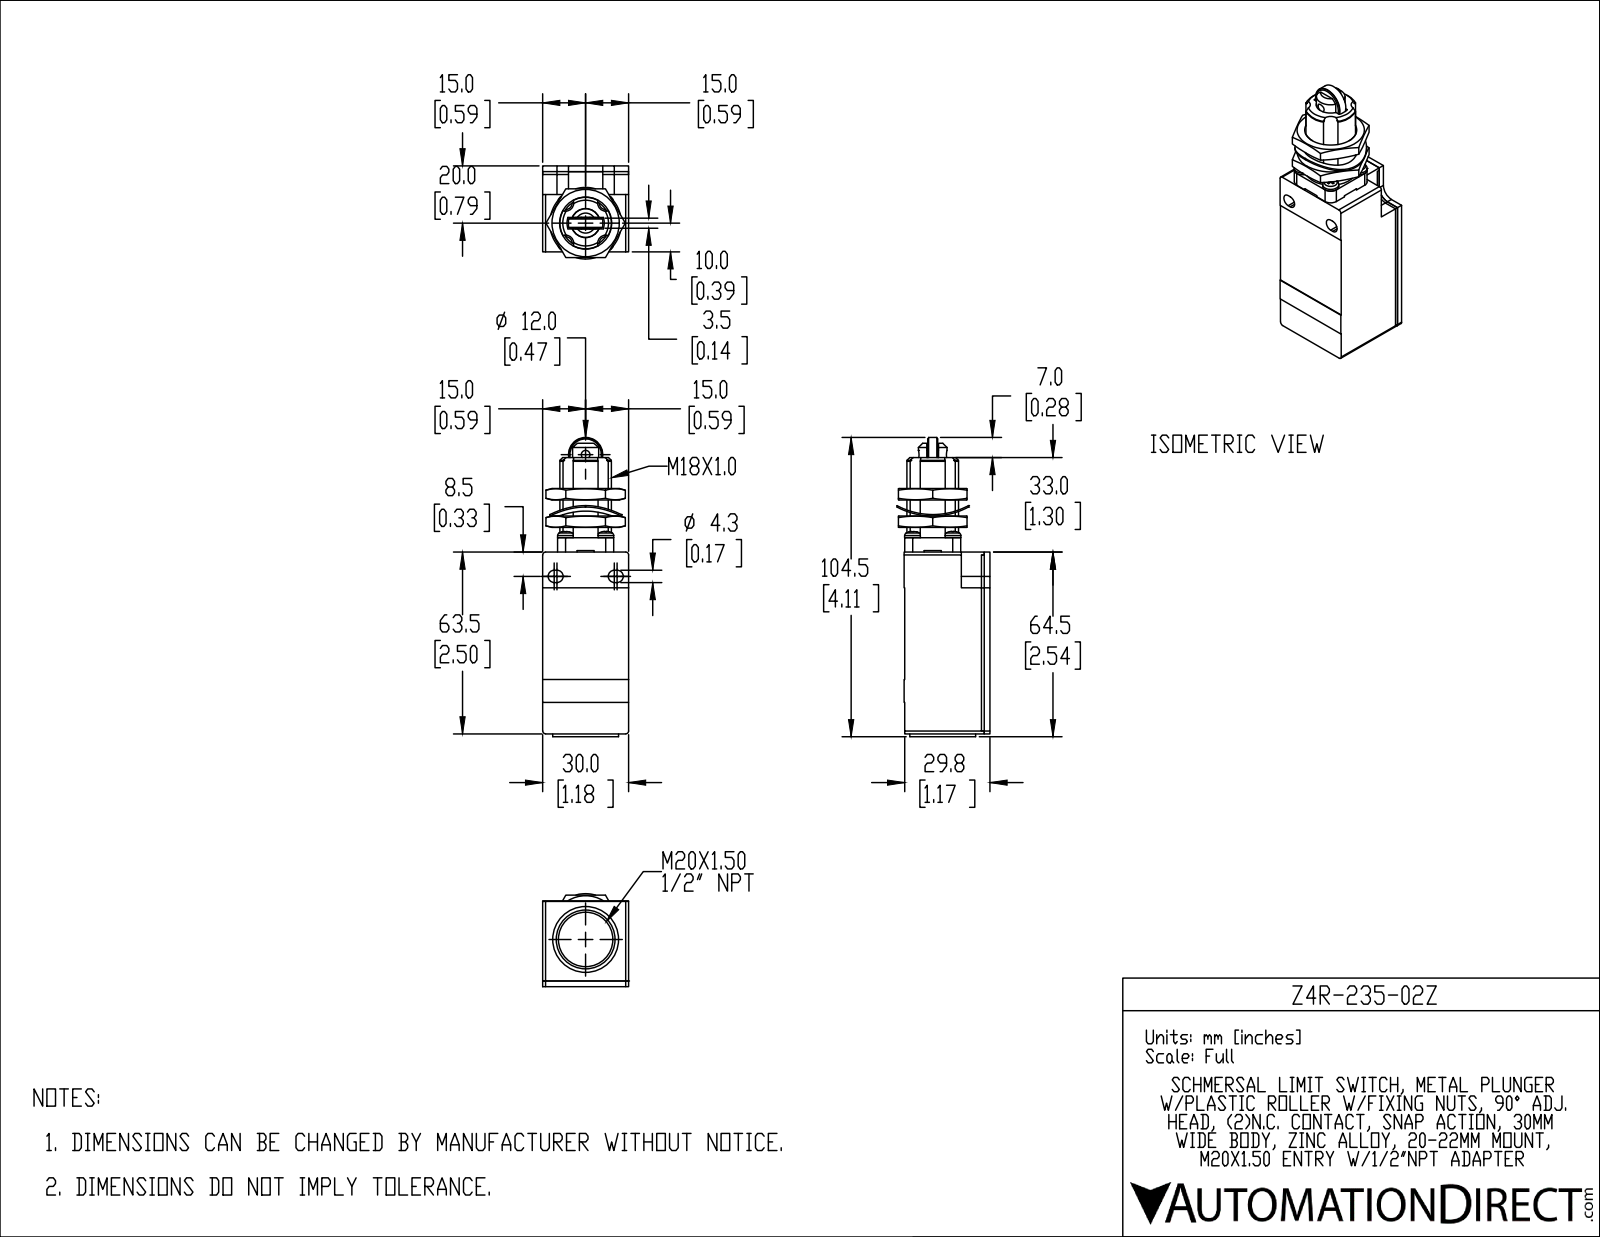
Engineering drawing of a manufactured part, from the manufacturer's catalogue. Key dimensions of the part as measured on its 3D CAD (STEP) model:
Part name (STEP PRODUCT): Z4R-235-02Z
STEP written by: SolidWorks 2019 (AUTOMOTIVE_DESIGN)
Units: inches
Bodies: 2 solids, 388 faces (264 planar, 95 cylindrical, 29 other)
Overall size (bounding box): 4.114 × 1.279 × 1.181
Volume: 3.806 in³ · Surface area: 26.23 in²
Round holes (diameter × count): ⌀0.276 ×3, ⌀0.118 ×1, ⌀0.512 ×1, ⌀0.545 ×1, ⌀0.732 ×1, ⌀0.748 ×1
Round bosses / shafts (diameter × count): ⌀0.213 ×4, ⌀0.256 ×3, ⌀0.984 ×1, ⌀0.906 ×1, ⌀0.472 ×1, ⌀0.415 ×1, ⌀0.394 ×1, ⌀0.276 ×1
Partial cylindrical surfaces — rounded edges, fillets, slot ends (radius × count): R0.02 ×12, R0.039 ×4, R0.085 ×4, R0.11 ×4, R0.11 ×4, R0.157 ×2, R0.159 ×2, R1.043 ×2
Main face-to-face distances: 1.181, 1.173, 0.157, 2.5, 0.079, 0.378, 0.945, 0.207, 2.293, 0.15
Hole centre spacings: 2.228, 3.706, 0.138, 0.866, 1.496
